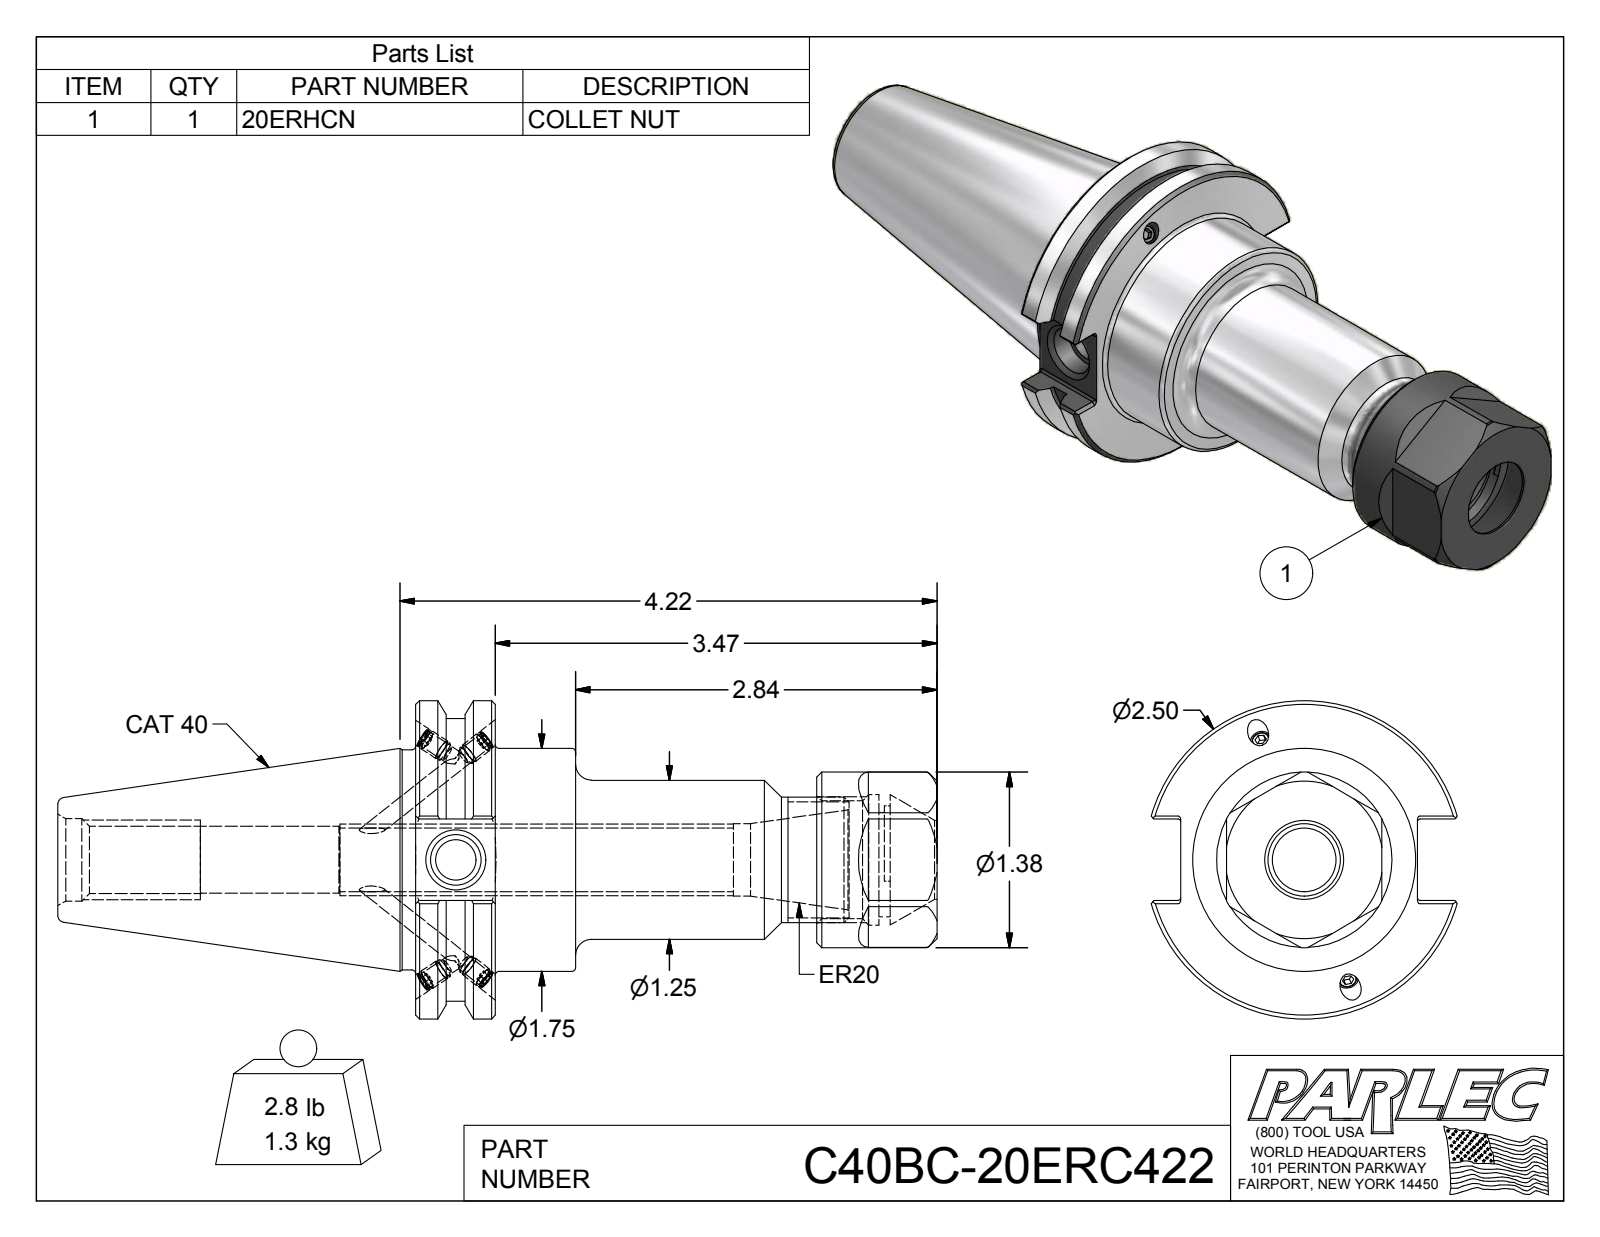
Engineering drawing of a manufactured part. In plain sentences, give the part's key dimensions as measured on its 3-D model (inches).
The part is named "C40BC-20ERC422; C40BCB-20ER4-1; 029-965; 20ERHCN". Its 3-D file was written by "Autodesk Inventor 2012 (AUTOMOTIVE_DESIGN)". It is 6 solids with 206 faces: 94 planar, 55 cylindrical and 57 other. Overall it measures 6.908 by 2.5 by 2.403 inches. Its volume is 10.02 cubic inches and its surface area 57.53 square inches. Round holes: 4 of diameter 0.13, 4 of diameter 0.161, 1 of diameter 0.315, 1 of diameter 0.399, 1 of diameter 0.502, 1 of diameter 0.526, 1 of diameter 0.527, 1 of diameter 0.57, 1 of diameter 0.62, 1 of diameter 0.648, 1 of diameter 0.82, 1 of diameter 0.925. Round bosses or shafts: 4 of diameter 0.165, 4 of diameter 0.157, 1 of diameter 2.5, 1 of diameter 2.219, 1 of diameter 1.75, 1 of diameter 1.73, 1 of diameter 1.378, 1 of diameter 1.25. Partial cylindrical surfaces (rounded edges, fillets, slot ends): 12 of radius 0.02, 1 of radius 0.423. The main face-to-face distances are 0.625, 1.22, 4.095, 3.47, 3.15, 2.525, 0.945, 1.255, 0.63, 1.895. The hole center spacings are 0.037.
